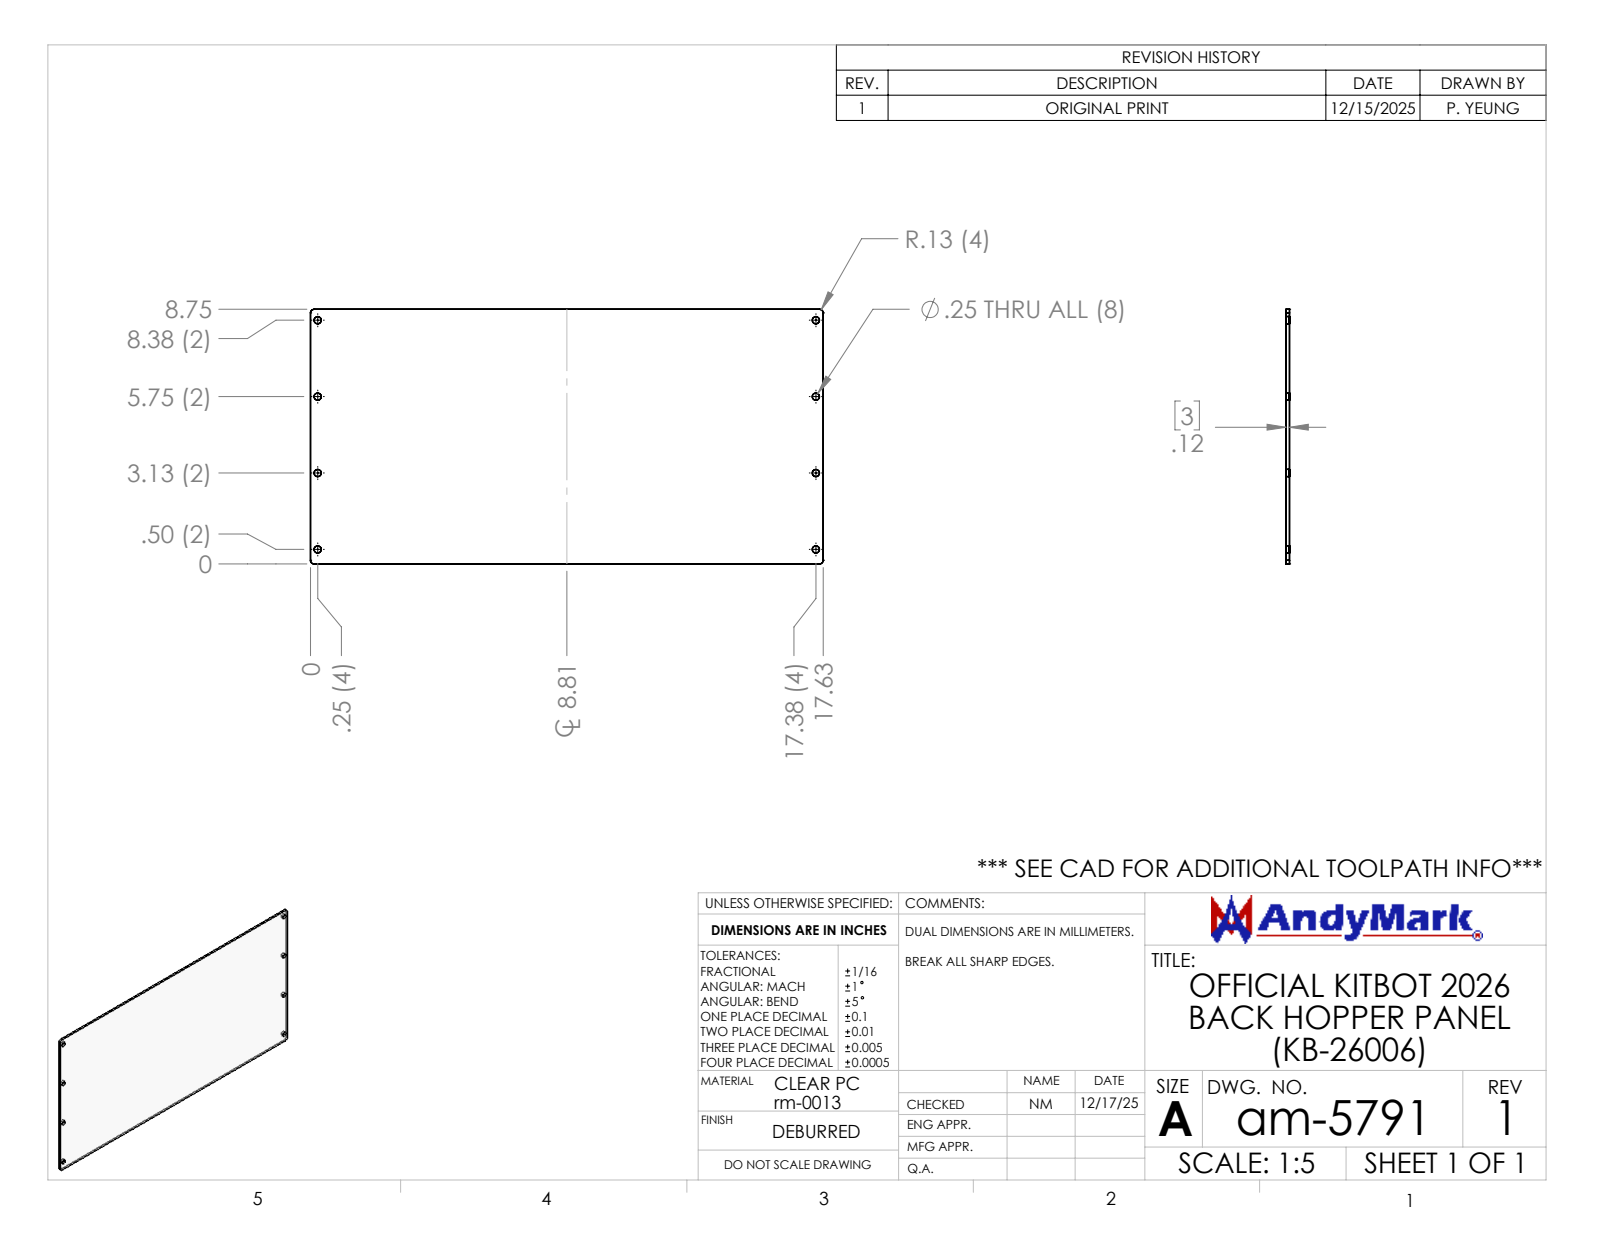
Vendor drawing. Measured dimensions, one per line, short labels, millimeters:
name: am-5791 Back Hopper Panel (KB-26006)
written by: SolidWorks 2024 (AUTOMOTIVE_DESIGN)
unit: mm
bodies: 1 solid, 26 faces (6 planar, 20 cylindrical, 0 other)
size: 447.7 × 222.3 × 3
volume: 297 800 mm³; area: 203 000 mm²
holes: 8× ⌀6.4
rounds: 4× R3.2
face distances: 3, 222.3, 447.7
hole spacings: 440.1, 66.7, 133.4, 435, 454.9, 66.7, 200, 478.8
